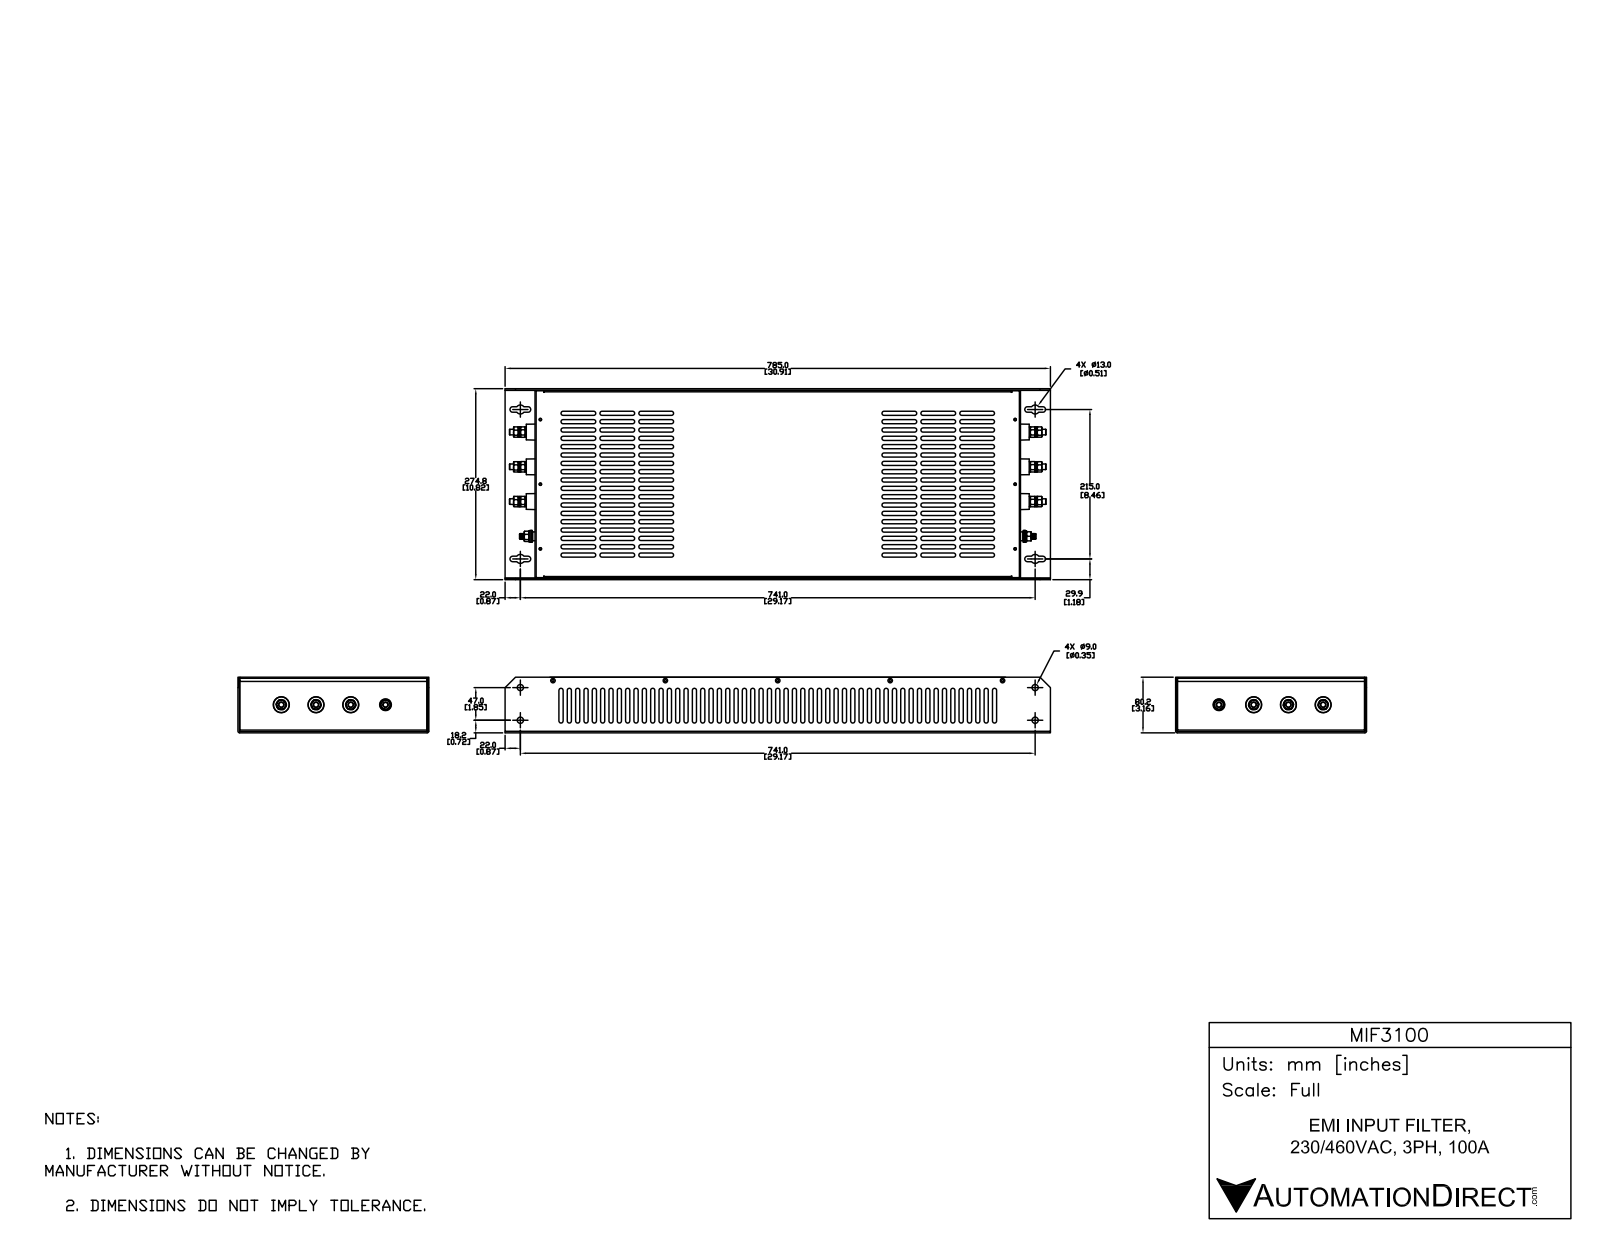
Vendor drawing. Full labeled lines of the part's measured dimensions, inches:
Part name (STEP PRODUCT): MIF3100 r1
STEP written by: SolidWorks 2017 (AUTOMOTIVE_DESIGN)
Units: inches
Bodies: 66 solids, 3555 faces (1360 planar, 1198 cylindrical, 997 other)
Overall size (bounding box): 30.906 × 10.819 × 3.157
Volume: 57.44 in³ · Surface area: 1 800 in²
Round holes (diameter × count): ⌀0.13 ×11, ⌀0.138 ×6, ⌀0.268 ×4, ⌀0.354 ×4, ⌀0.315 ×3, ⌀0.331 ×3, ⌀0.472 ×3, ⌀0.48 ×3, ⌀0.335 ×1
Round bosses / shafts (diameter × count): ⌀0.234 ×8, ⌀0.197 ×8, ⌀0.579 ×3, ⌀0.663 ×1, ⌀0.622 ×1, ⌀0.512 ×1, ⌀0.498 ×1, ⌀0.412 ×1
Partial cylindrical surfaces — rounded edges, fillets, slot ends (radius × count): R0.118 ×326, R0.128 ×8, R0.157 ×8, R0.016 ×6, R0.079 ×6, R0.107 ×5, R0.031 ×4, R0.063 ×4
Main face-to-face distances: 0.079, 0.047, 3.031, 3.11, 3.157, 3.079, 10.74, 10.661, 10.819, 27.346
Hole centre spacings: 3.661, 6.37, 27.154, 1.969, 12.74, 26.906, 1.85, 1.888
